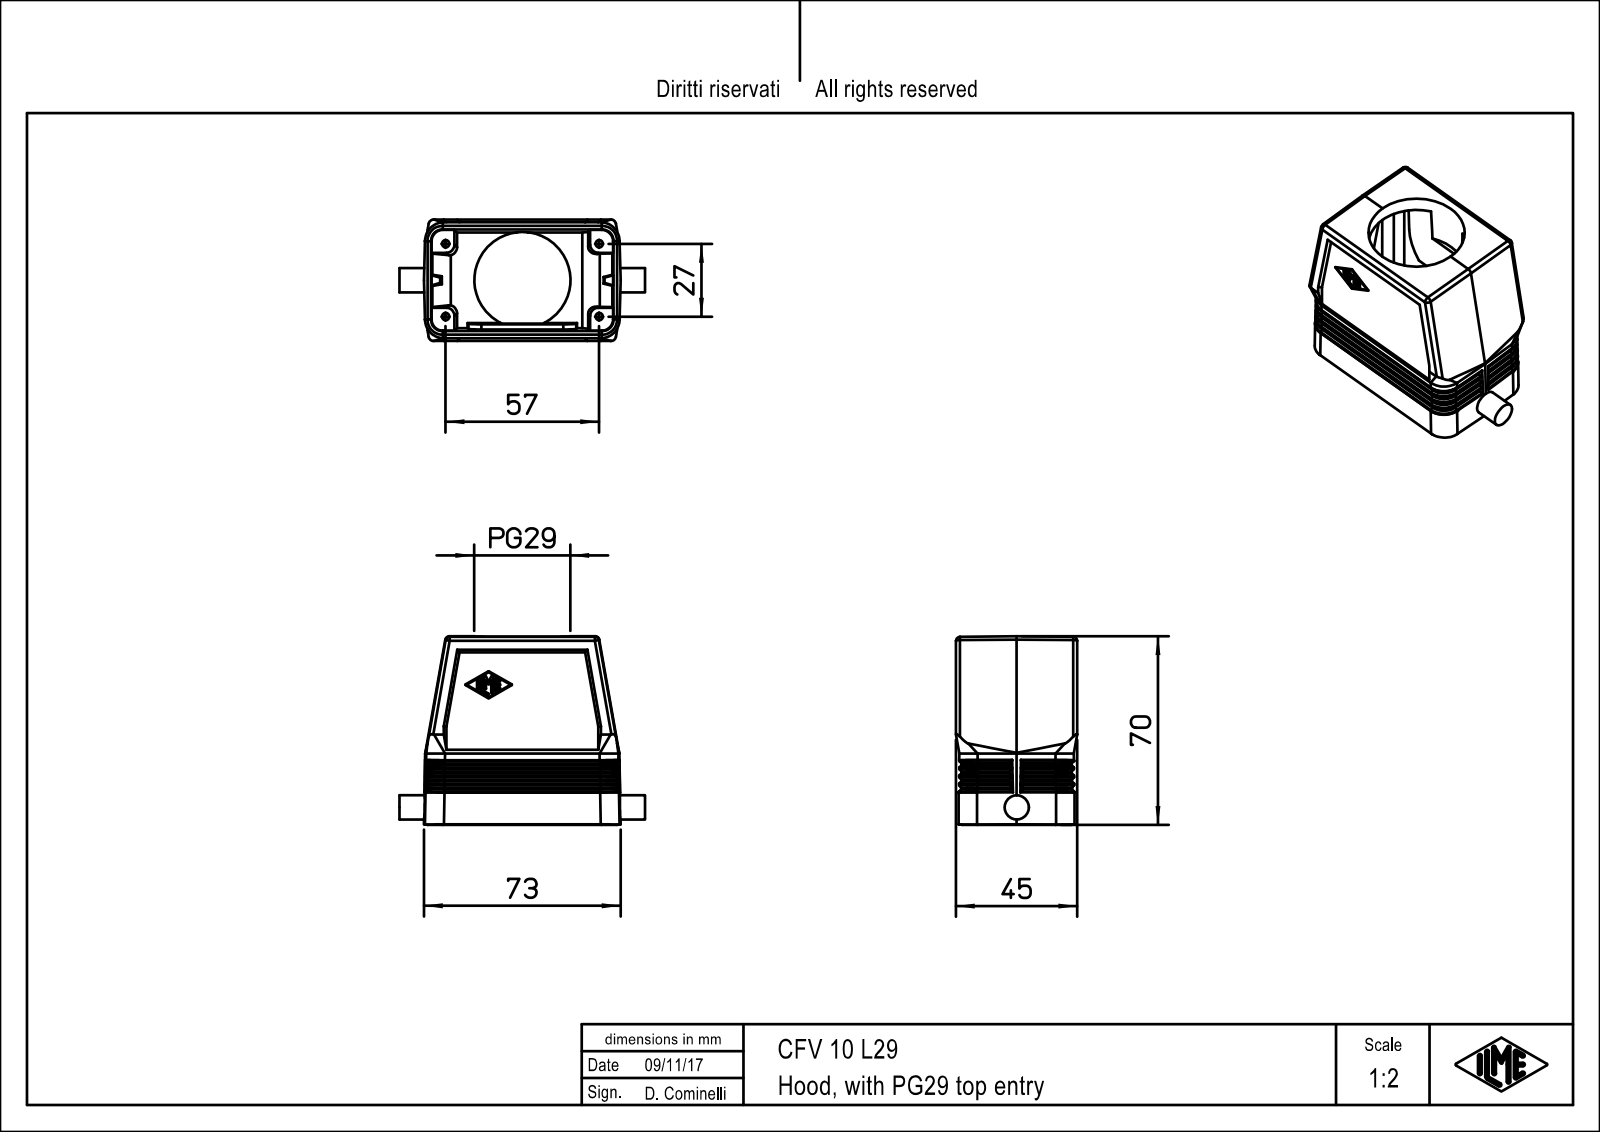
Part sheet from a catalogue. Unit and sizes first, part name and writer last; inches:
Units: inches
Overall size (bounding box): 3.59 × 2.756 × 1.772
Round holes (diameter × count): ⌀0.108 ×4, ⌀0.189 ×1, ⌀1.406 ×1
Round bosses / shafts (diameter × count): ⌀0.354 ×1, ⌀0.126 ×1
Partial cylindrical surfaces — rounded edges, fillets, slot ends (radius × count): R0.02 ×16, R0.059 ×10, R0.276 ×8, R0.118 ×4, R0.165 ×4, R0.787 ×1
Main face-to-face distances: 1.693, 0.335, 0.079, 0.075, 1.732, 0.039, 0.157, 1.772, 0.236, 0.447
Hole centre spacings: 1.242, 1.063, 2.244, 2.483
Volume: 3.98 in³ · Surface area: 50.76 in²
Bodies: 1 solid, 348 faces (144 planar, 70 cylindrical, 134 other)
Part name (STEP PRODUCT): CFV_10_L29
STEP written by: PTC Creo Elements/Direct Modeling 19.0E 27-Jun-2016 (C) Parametric Technology GmbH (AUTOMOTIVE_DESIGN)
